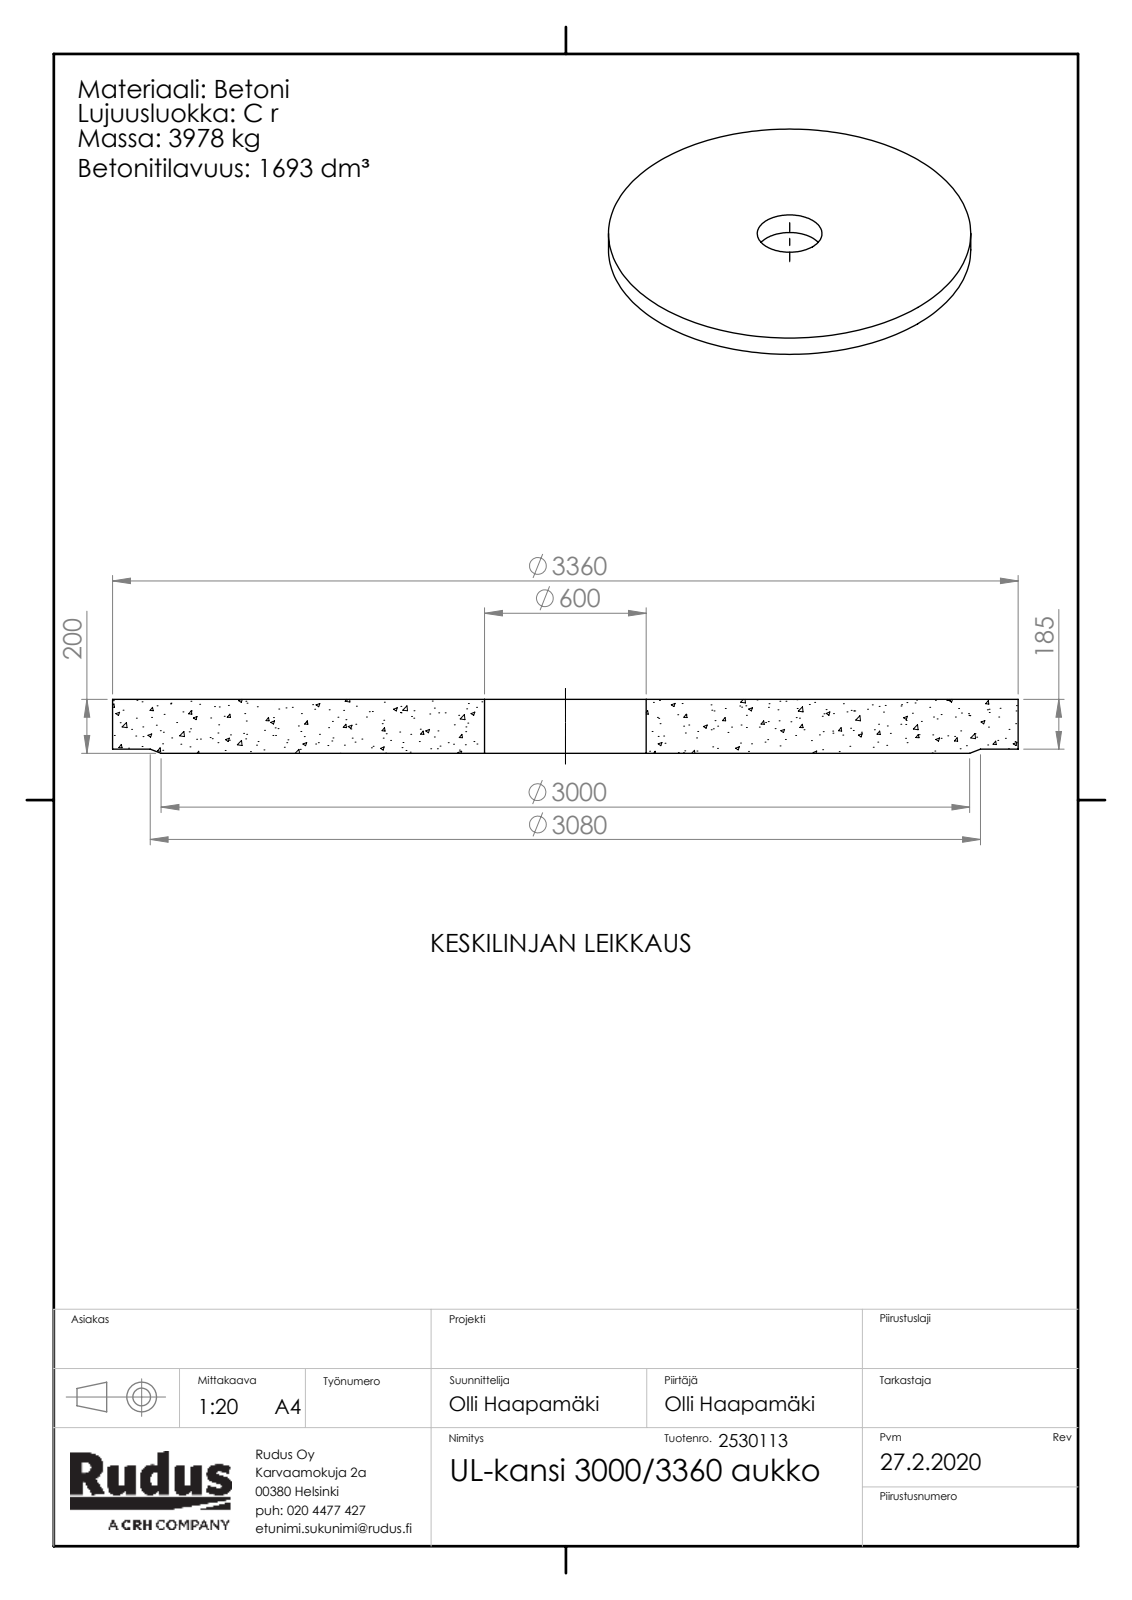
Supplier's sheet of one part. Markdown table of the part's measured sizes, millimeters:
| quantity | value |
| --- | --- |
| part name | UL-osa-kansi_aukko; Rudus 2530113 UL-kansi 3000_3360 aukko |
| STEP written by | SolidWorks 2019 (CONFIG_CONTROL_DESIGN) |
| units | millimeters |
| bodies | 1 solid, 9 faces (3 planar, 4 cylindrical, 2 other) |
| overall size | 3360 × 3360 × 200 |
| volume | 1 693 000 000 mm³ |
| surface area | 19 520 000 mm² |
| round holes (diameter × count) | 600 × 1 |
| round bosses / shafts (diameter × count) | 3360 × 1 |
| main face-to-face distances | 200, 15, 185 |
